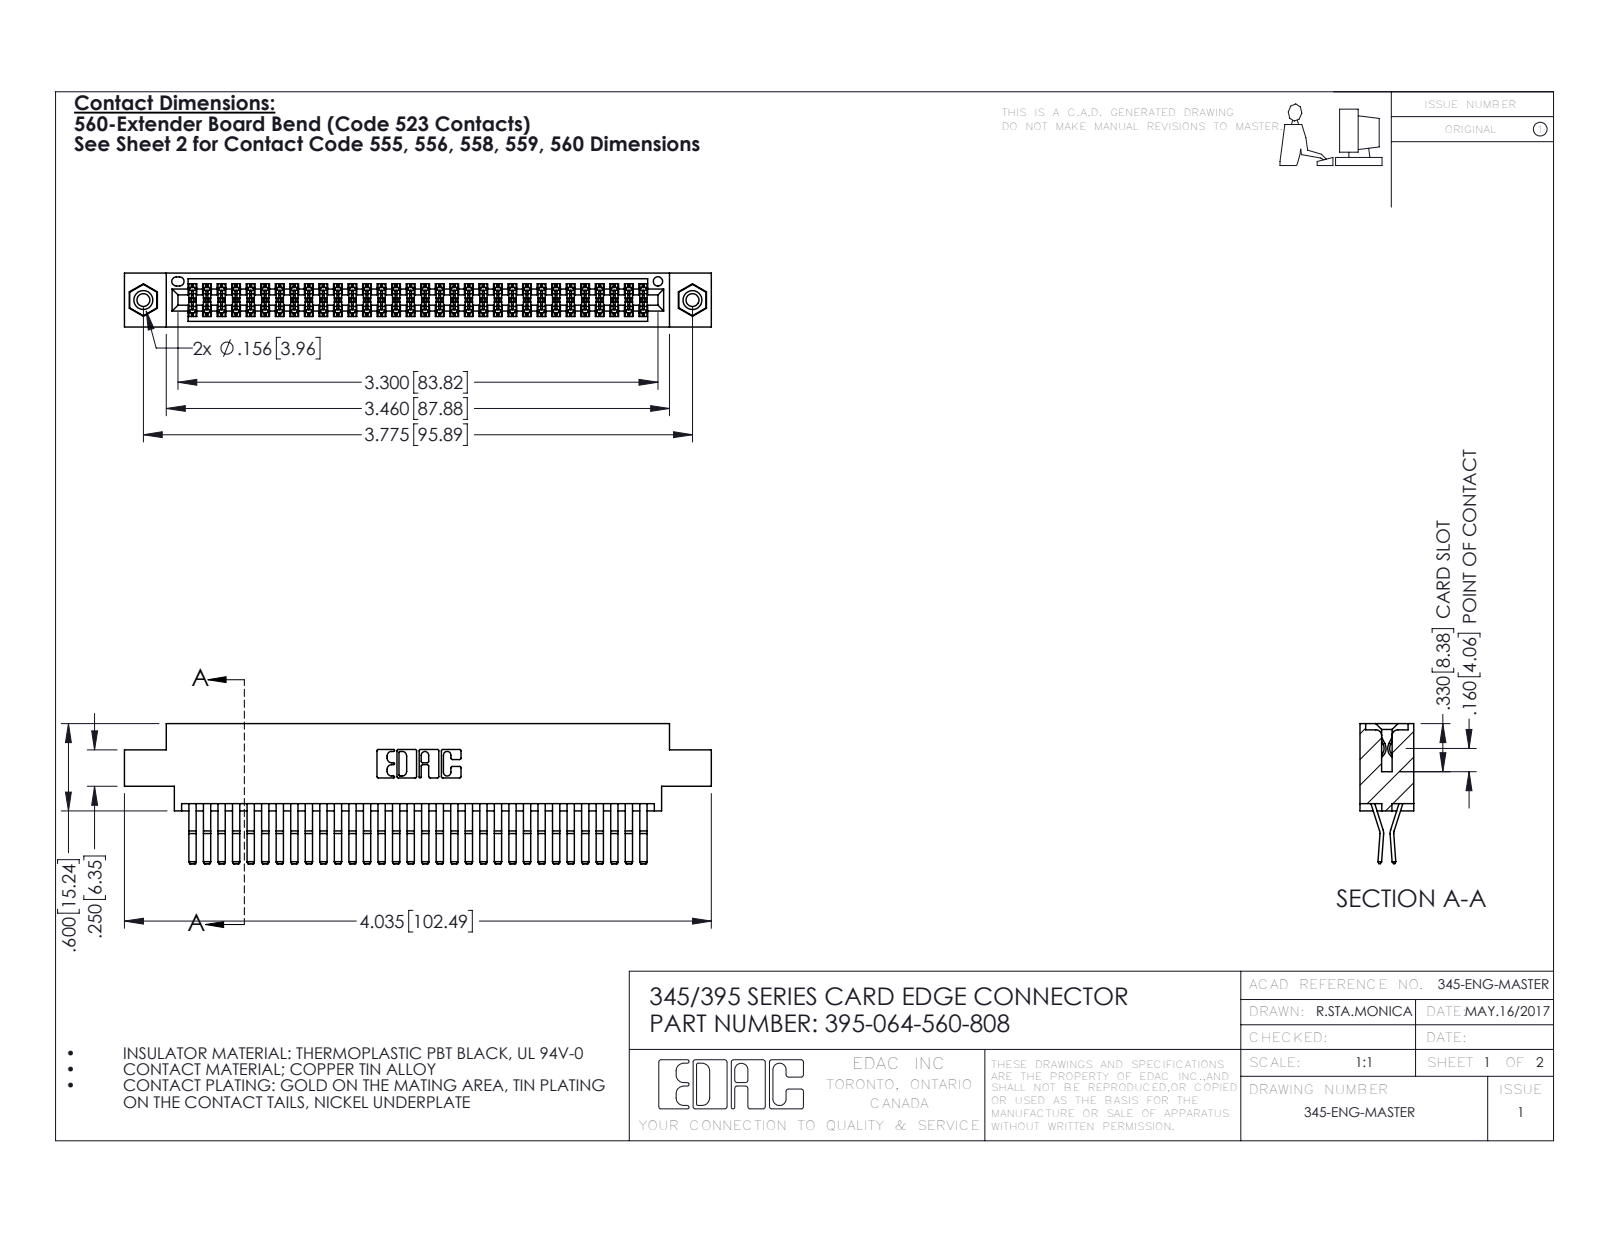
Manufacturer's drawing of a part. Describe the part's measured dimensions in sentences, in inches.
The part is named "345-250-001_345-250-003-102; 395-064-560-808; 345 Part_0.170 Offset - 0.156 Dia-TI; 345-292-001_560 Tail". Its 3-D file was written by "SolidWorks 2016 (CONFIG_CONTROL_DESIGN)". It is 67 solids with 3518 faces: 2228 planar, 1274 cylindrical and 16 other. Overall it measures 4.035 by 0.962 by 0.37 inches. Its volume is 0.62 cubic inches and its surface area 24.9 square inches. Round holes: 2 of diameter 0.089, 2 of diameter 0.125, 2 of diameter 0.156, 1 of diameter 0.064. Round bosses or shafts: 2 of diameter 0.155. Partial cylindrical surfaces (rounded edges, fillets, slot ends): 97 of radius 0.006, 22 of radius 0.01, 6 of radius 0.007, 6 of radius 0.031, 3 of radius 0.026, 2 of radius 0.01, 2 of radius 0.014, 2 of radius 0.019. The main face-to-face distances are 0.025, 0.072, 0.298, 0.37, 0.2, 0.098, 0.272, 0.225, 0.175, 0.149. The hole center spacings are 0.27, 3.54, 3.775.
